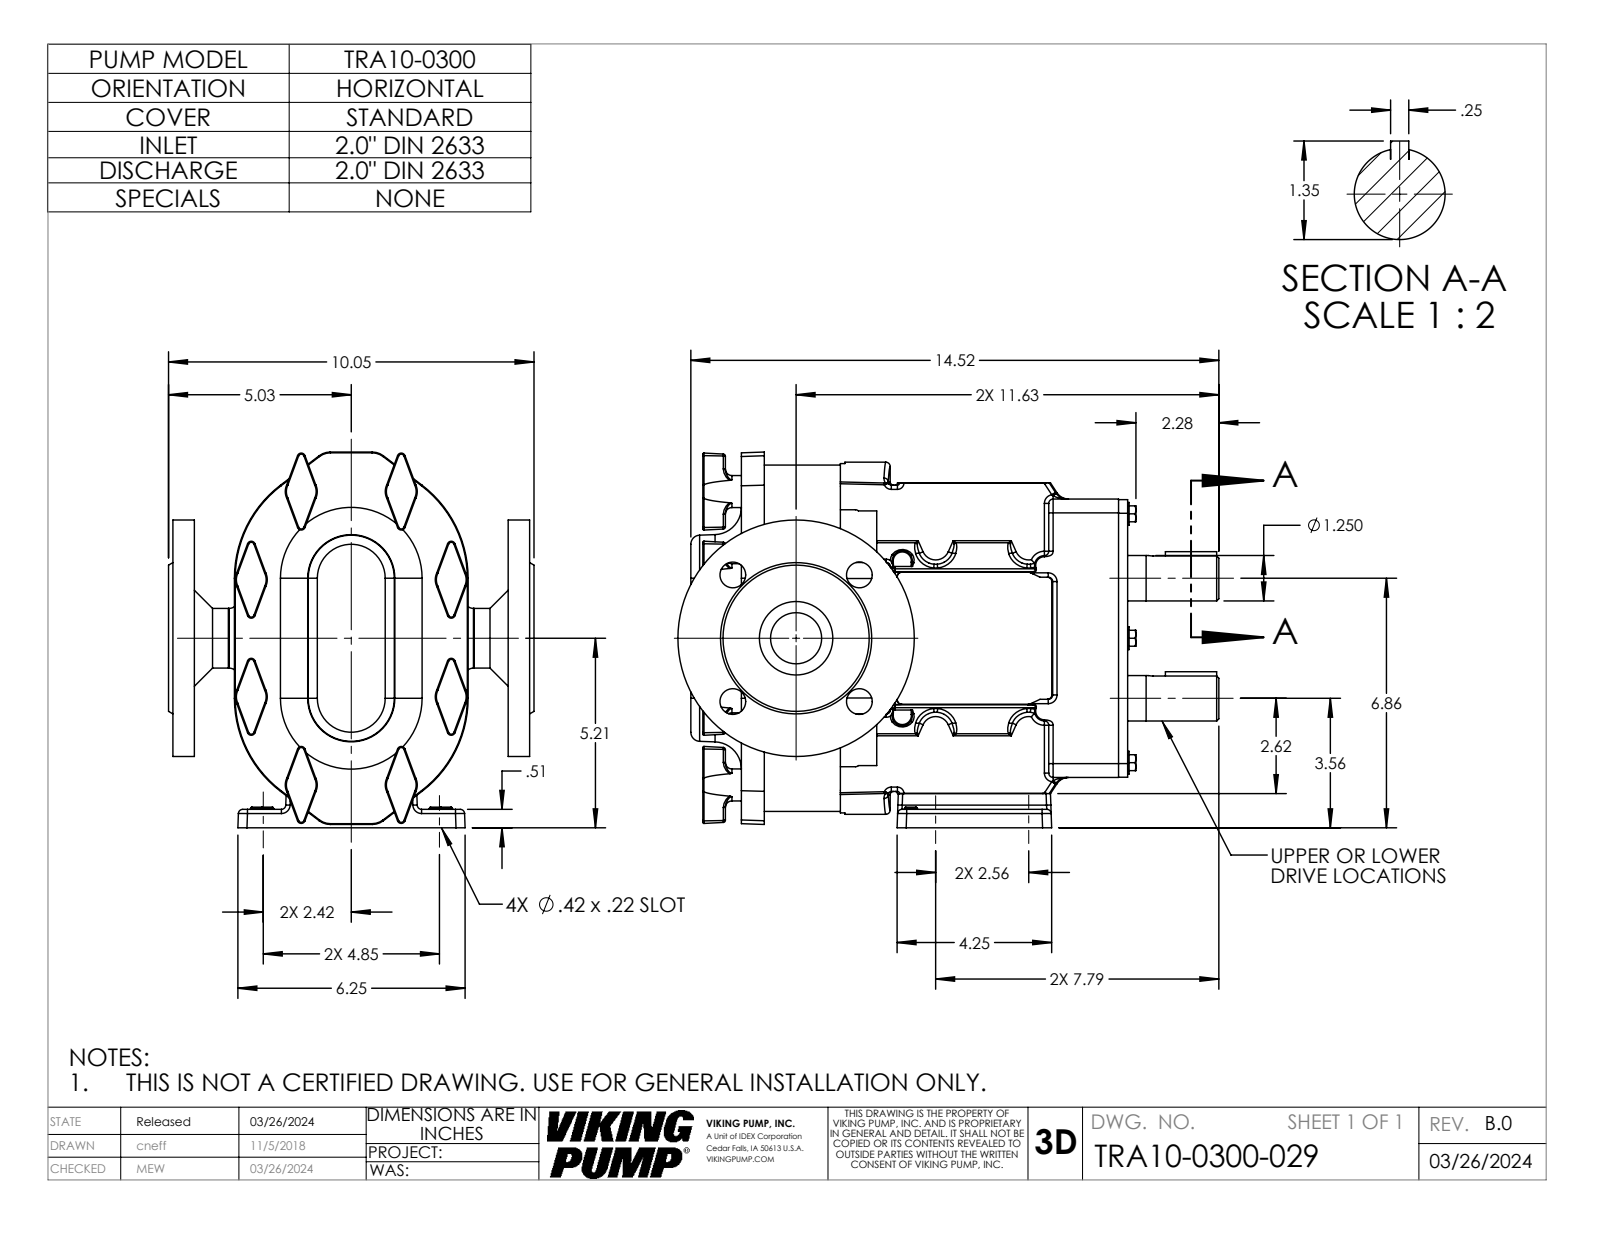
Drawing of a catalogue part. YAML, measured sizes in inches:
part_name: "0300DIN2633-20; TRA10-0300-BODY; TRA10-0300-GEARBOX-H; TRA10-0300-COVER-STD (+1 more)"
step_written_by: "SolidWorks 2022 (AUTOMOTIVE_DESIGN)"
units: inches
bodies: {solids: 5, faces: 1104, planar: 285, cylindrical: 369, other: 450}
overall_size: [14.876, 10.328, 10.05]
volume: 498.7
surface_area: 899.3
round_holes:
  - {diameter: 0.709, count: 4}
  - {diameter: 1.406, count: 1}
  - {diameter: 2.02, count: 1}
round_bosses_or_shafts:
  - {diameter: 0.88, count: 8}
  - {diameter: 0.625, count: 6}
  - {diameter: 1.249, count: 2}
  - {diameter: 6.5, count: 1}
  - {diameter: 1.64, count: 1}
partial_cylinders:
  - {radius: 0.12, count: 90}
  - {radius: 0.03, count: 50}
  - {radius: 0.06, count: 44}
  - {radius: 0.09, count: 10}
  - {radius: 0.219, count: 8}
  - {radius: 0.375, count: 8}
  - {radius: 0.38, count: 8}
  - {radius: 0.5, count: 8}
face_to_face_distances: [2.092, 0.59, 9.22, 3.093, 6.717, 2.503, 6.127, 9.992, 7.9, 7.525]
hole_center_spacings: [2.46, 2.461, 3.48, 3.48, 4.921]
